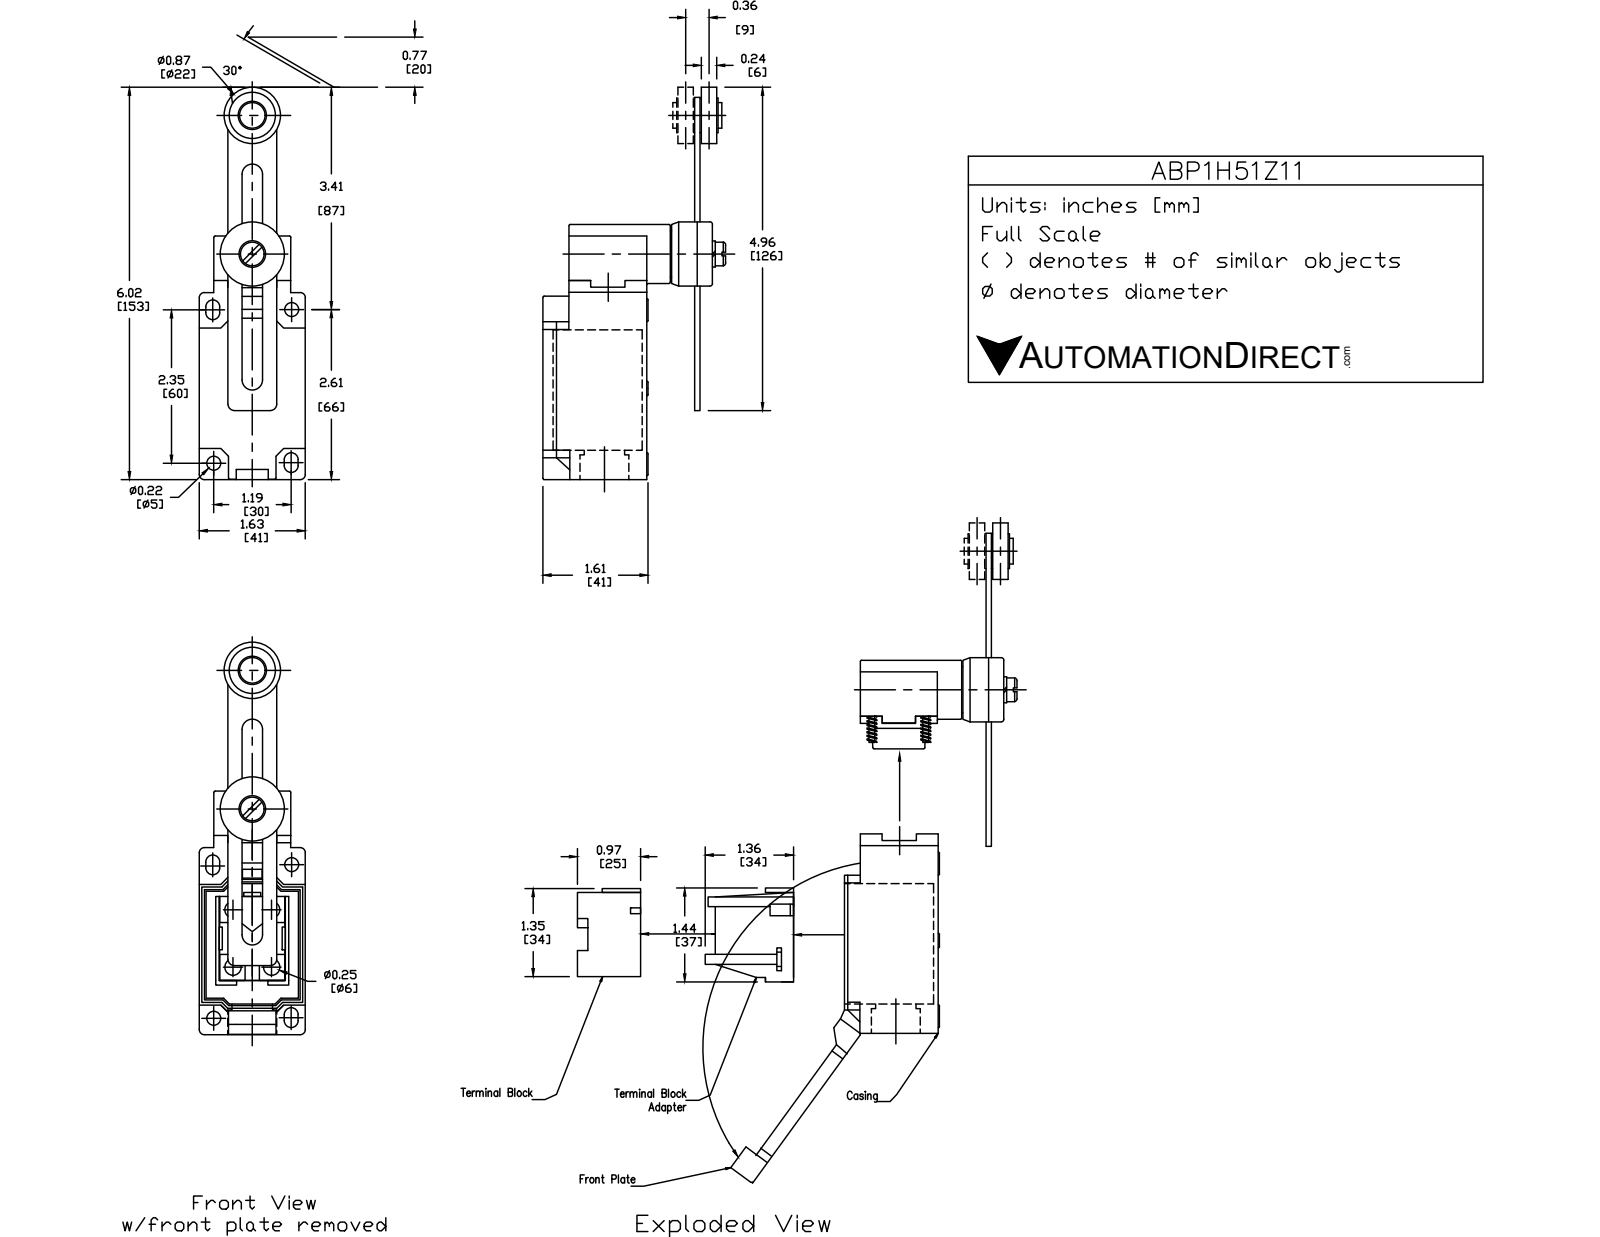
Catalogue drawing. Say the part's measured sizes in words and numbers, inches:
The part is named "ABP1H51Z11". Its 3-D file was written by "SolidWorks 2017 (AUTOMOTIVE_DESIGN)". It is 7 solids with 248 faces: 135 planar, 91 cylindrical and 22 other. Overall it measures 6.39 by 2.414 by 1.614 inches. Its volume is 8.883 cubic inches and its surface area 50.28 square inches. Round holes: 2 of diameter 0.213, 1 of diameter 0.236, 1 of diameter 0.551, 1 of diameter 0.669, 1 of diameter 0.748. Round bosses or shafts: 5 of diameter 0.354, 2 of diameter 0.394, 1 of diameter 0.984, 1 of diameter 0.906, 1 of diameter 0.866, 1 of diameter 0.709, 1 of diameter 0.276. Partial cylindrical surfaces (rounded edges, fillets, slot ends): 16 of radius 0.02, 4 of radius 0.079, 4 of radius 0.106, 2 of radius 0.118, 2 of radius 0.159, 1 of radius 0.276, 1 of radius 0.453, 1 of radius 0.472. The main face-to-face distances are 1.614, 1.565, 0.435, 0.079, 1.921, 0.356, 2, 1.181, 0.217, 1.398. The hole center spacings are 1.042, 2.641, 3.274.
